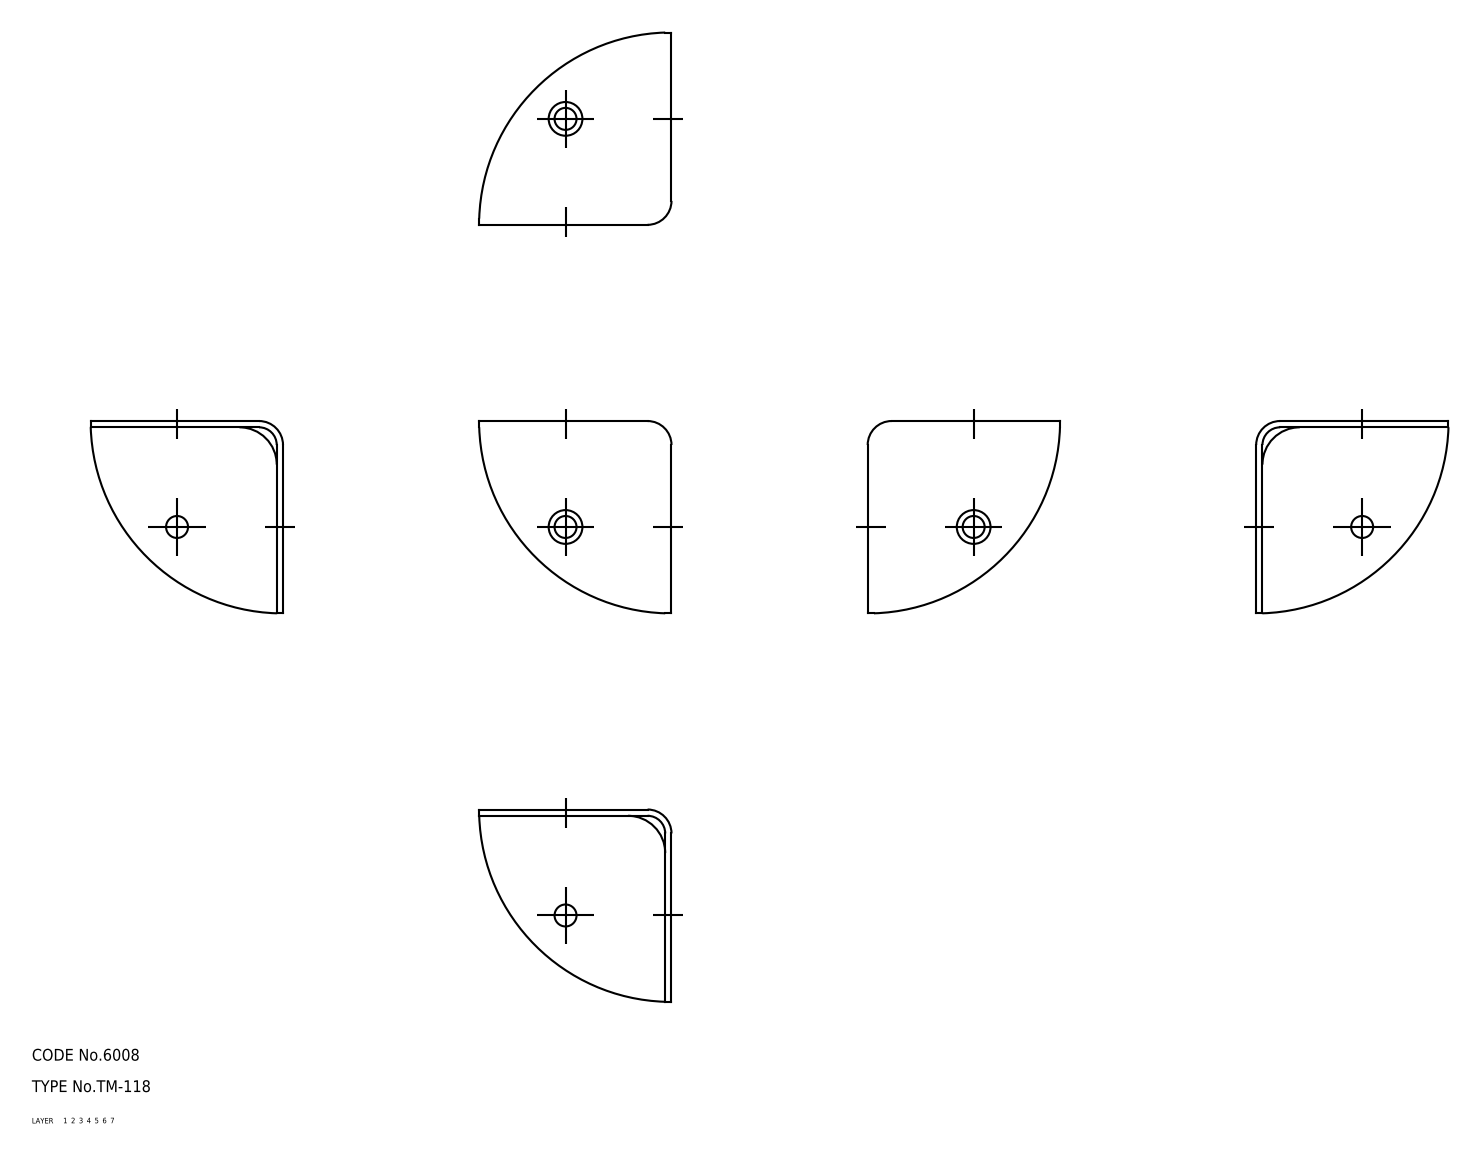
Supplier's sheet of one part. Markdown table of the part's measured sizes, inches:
| quantity | value |
| --- | --- |
| part name | angle |
| STEP written by | CADfix (AUTOMOTIVE_DESIGN) |
| units | inches |
| bodies | 1 solid, 29 faces (0 planar, 0 cylindrical, 29 other) |
| overall size | 1.929 × 1.929 × 1.929 |
| volume | 0.464 in³ |
| surface area | 15.49 in² |
